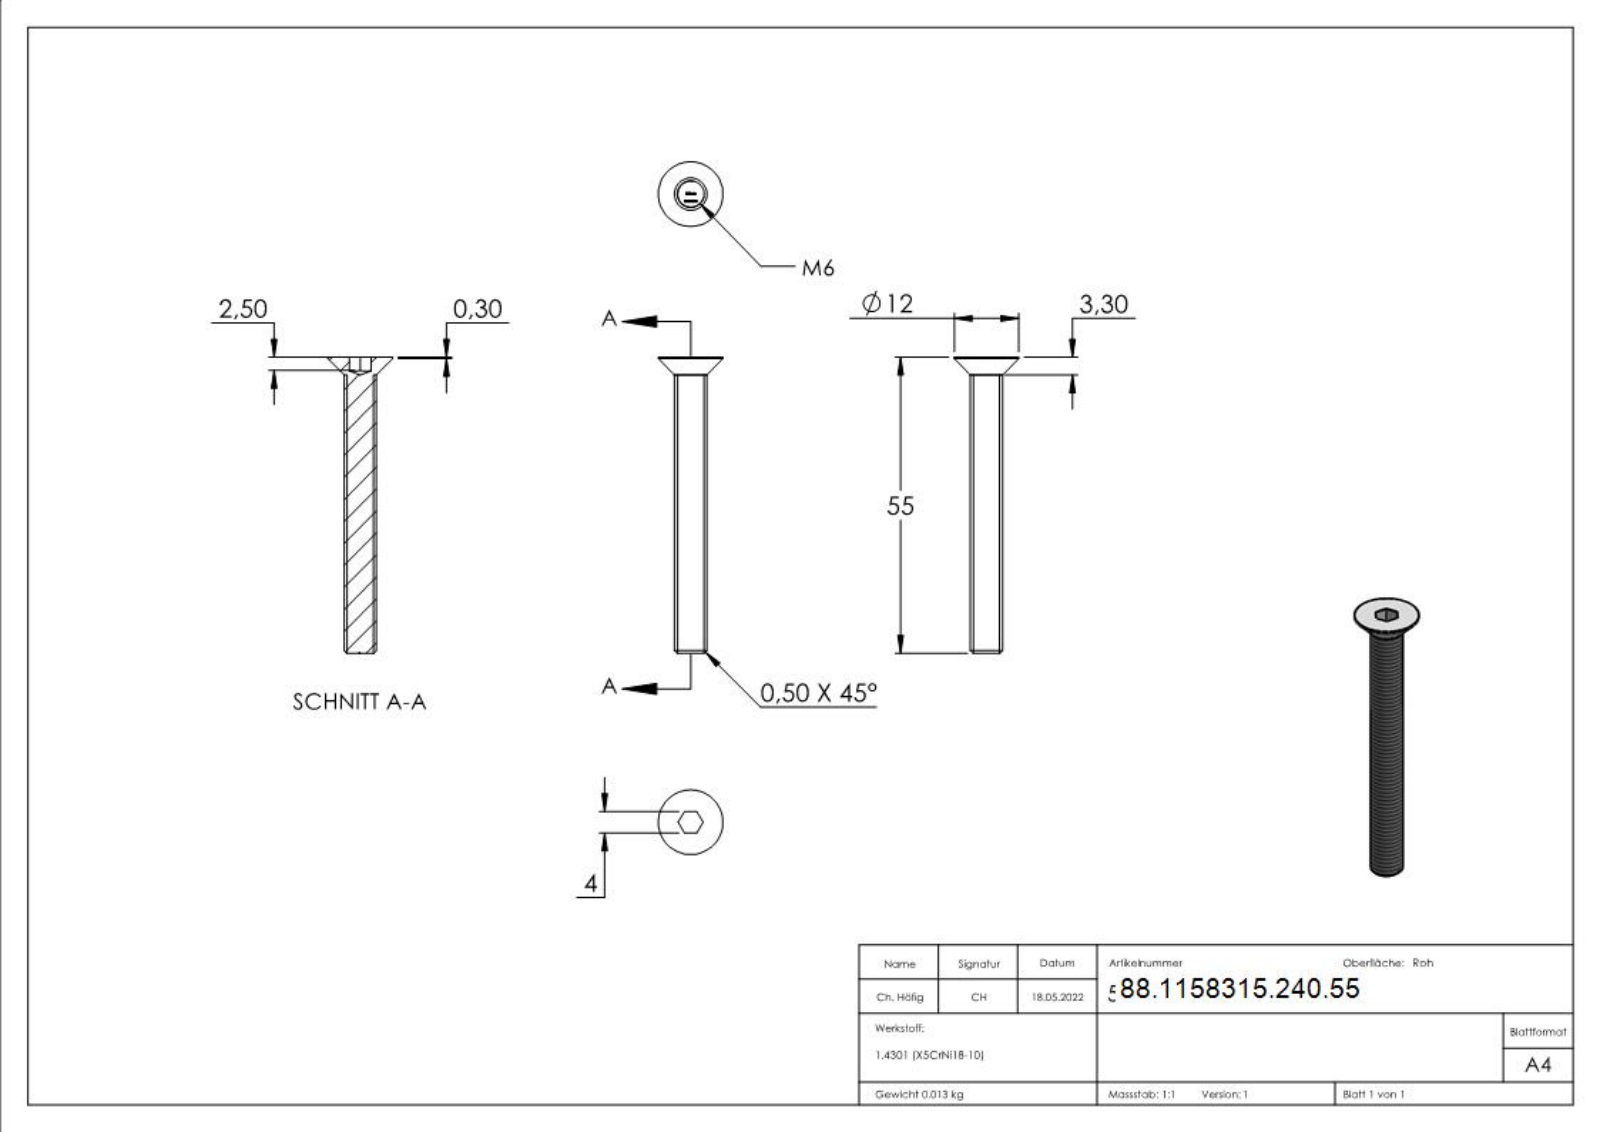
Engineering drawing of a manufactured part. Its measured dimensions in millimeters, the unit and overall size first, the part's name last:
Units: millimetres
Overall size (bounding box): 55 × 12 × 12
Round bosses / shafts (diameter × count): ⌀12 ×1, ⌀6 ×1
Main face-to-face distances: 55, 4, 54.9, 0.8, 0.82, 0.65, 0.33, 0.79, 1.44, 0.59
Volume: 1 652 mm³ · Surface area: 1 280 mm²
Bodies: 1 solid, 280 faces (149 planar, 2 cylindrical, 129 other)
Part name (STEP PRODUCT): 58315-240-55
STEP written by: SolidWorks 2018 (CONFIG_CONTROL_DESIGN)
